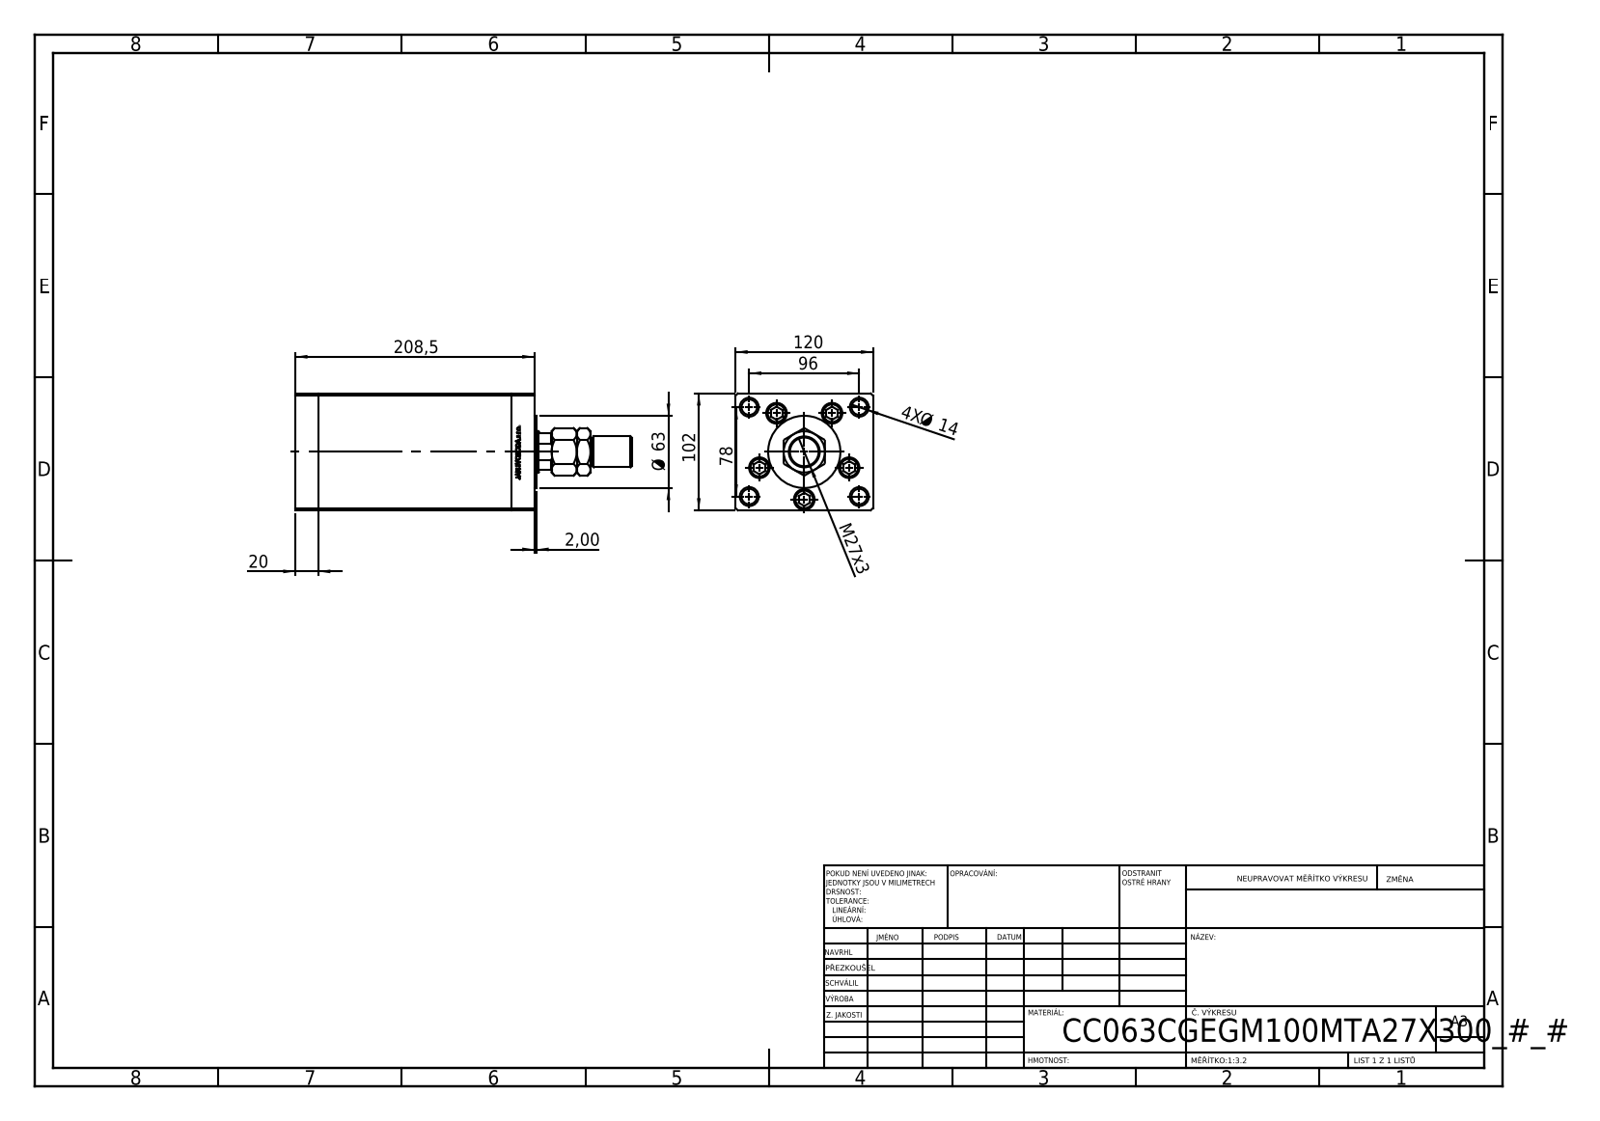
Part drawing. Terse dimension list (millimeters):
name: ALLEN BOLT; V220C BACK_C; MTA; V220C_VC_C (+2 more)
written by: SolidWorks 2019 (CONFIG_CONTROL_DESIGN)
unit: mm
bodies: 14 solids, 1214 faces (557 planar, 165 cylindrical, 492 other)
size: 293.5 × 120 × 102
volume: 2 199 000 mm³; area: 307 904 mm²
holes: 9× ⌀13.5, 5× ⌀18, 4× ⌀12, 4× ⌀16.5, 1× ⌀17, 1× ⌀25.5, 1× ⌀36
bosses: 5× ⌀8, 4× ⌀17, 1× ⌀63, 1× ⌀27, 1× ⌀25
rounds: 2× R0.93, 1× R17.5
face distances: 120, 102, 20, 168.5, 188.5, 34.25, 208.5, 174.25, 154.25, 14.25
hole spacings: 41.5, 61.85, 24.39, 26.69, 47.92, 48.07, 49.84, 53.57
